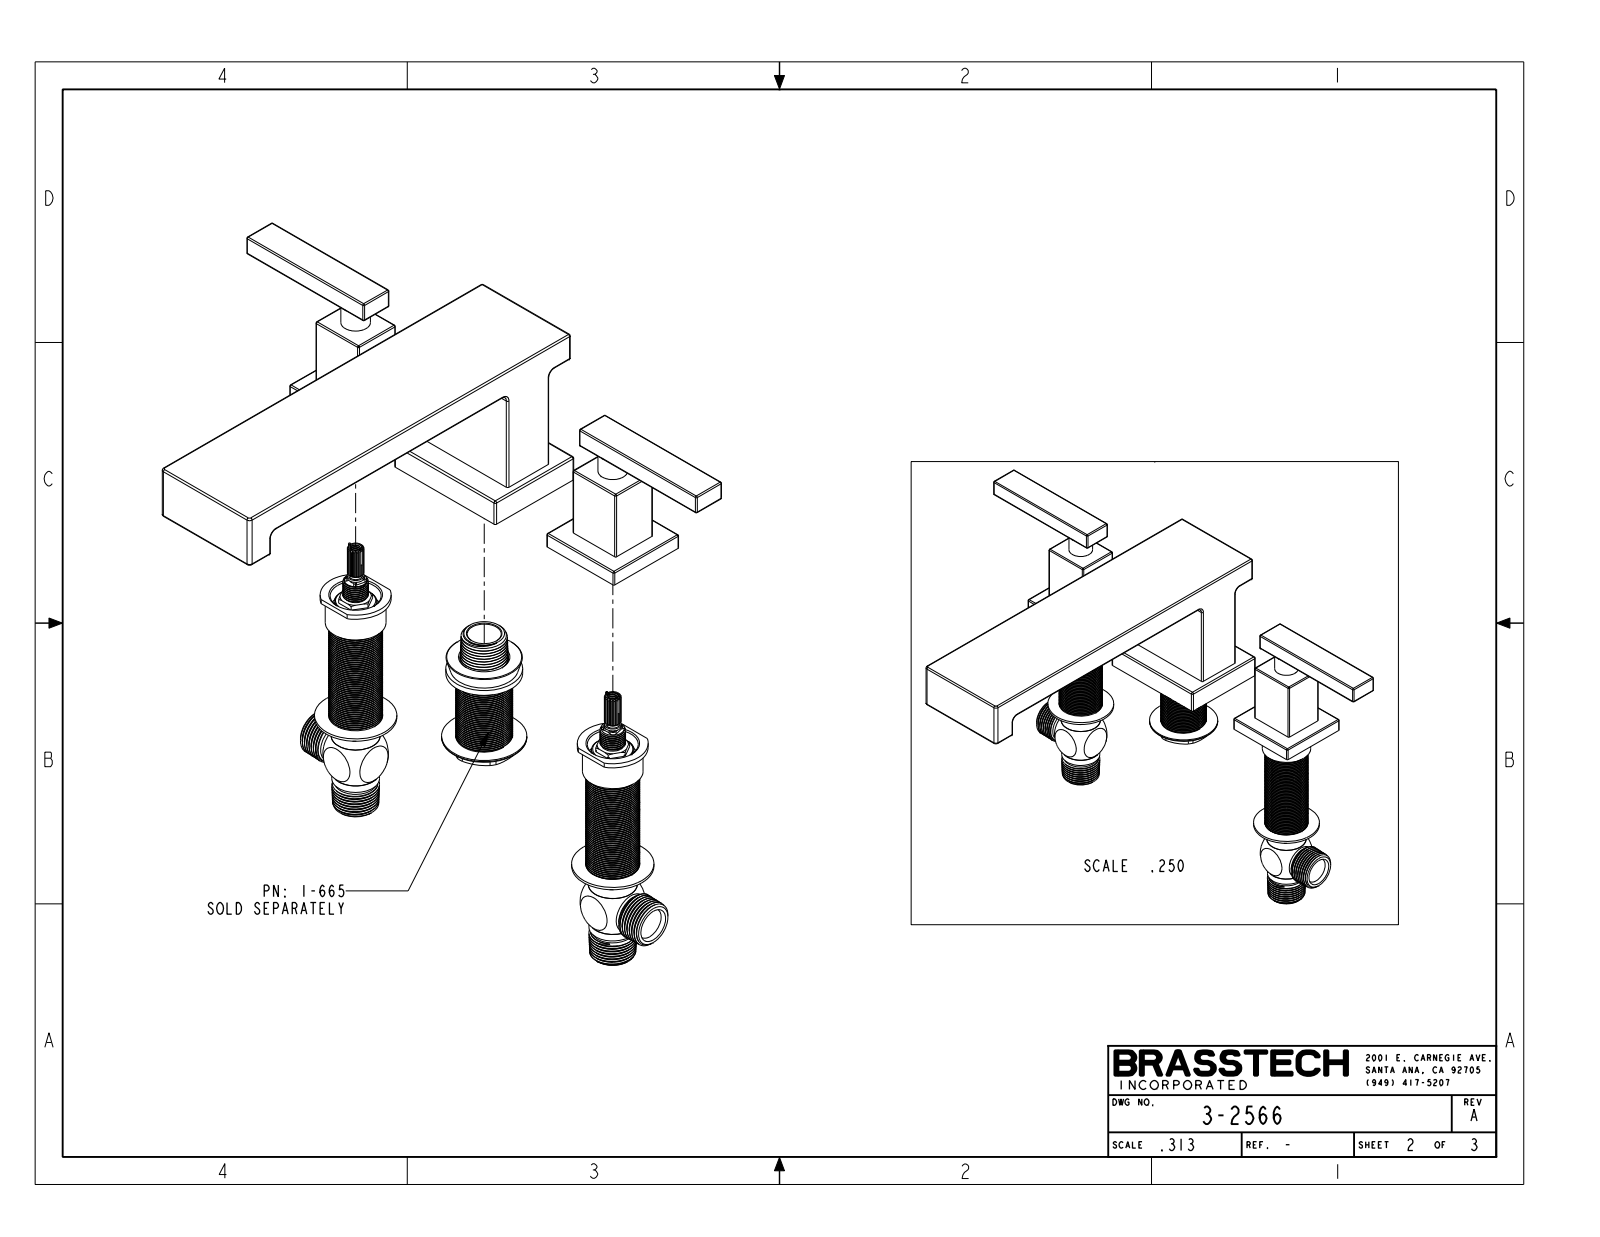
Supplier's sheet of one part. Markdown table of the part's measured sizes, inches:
| quantity | value |
| --- | --- |
| part name | 3-2566 |
| STEP written by | CREO PARAMETRIC BY PTC INC, 2018400 (CONFIG_CONTROL_DESIGN) |
| units | inches |
| bodies | 3 solids, 217 faces (55 planar, 102 cylindrical, 60 other) |
| overall size | 14 × 10 × 3.76 |
| volume | 44.43 in³ |
| surface area | 169.4 in² |
| round bosses / shafts (diameter × count) | 0.65 × 2, 0.523 × 2 |
| partial cylindrical surfaces (radius × count) | 0.03 × 48, 0.04 × 27, 0.16 × 3, 0.08 × 2 |
| main face-to-face distances | 0.67, 3.09, 3.76, 2.76, 1.16, 0.07, 1.23, 1.3, 0.25, 1.05 |
